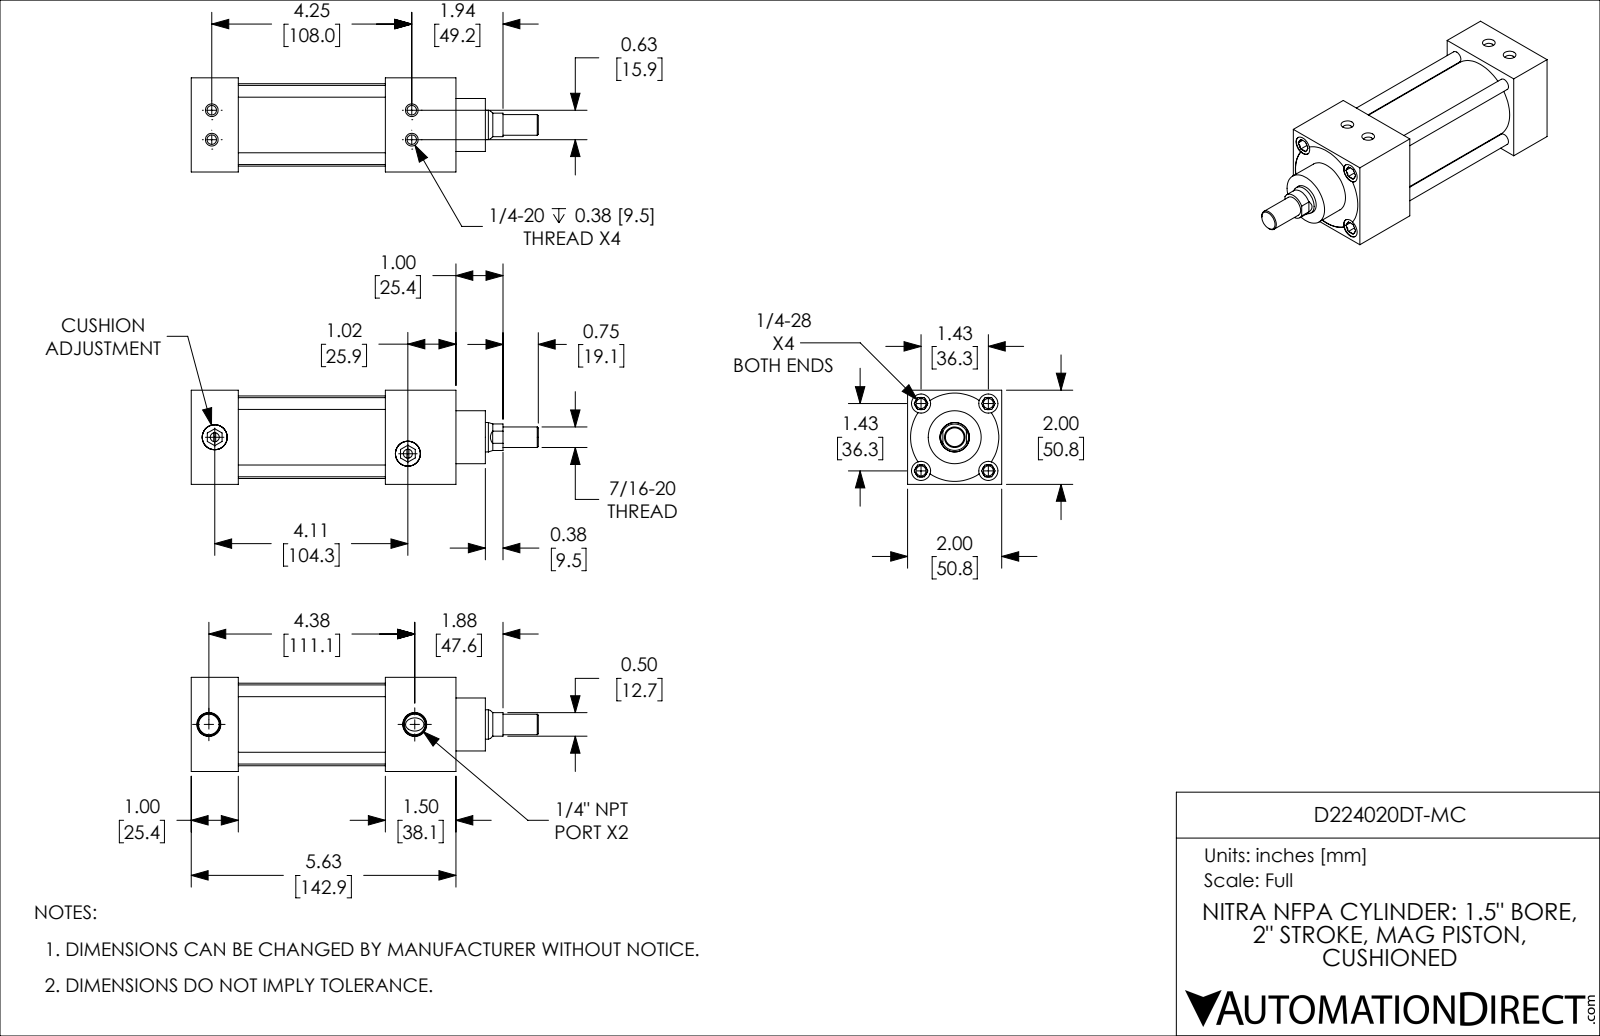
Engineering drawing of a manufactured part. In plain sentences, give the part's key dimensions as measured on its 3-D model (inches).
The part is named "D224020DT-MC_PISTON_KK1; D224020DT-MC; D224020DT-MC_CUSHION; D224020DT-MC_BODY". Its 3-D file was written by "SolidWorks 2019 (CONFIG_CONTROL_DESIGN)". It is 4 solids with 251 faces: 90 planar, 81 cylindrical and 80 other. Overall it measures 7.375 by 2 by 2 inches. Its volume is 15.46 cubic inches and its surface area 109.5 square inches. Round holes: 4 of diameter 0.201, 4 of diameter 0.213, 4 of diameter 0.406, 2 of diameter 0.19, 2 of diameter 0.438, 2 of diameter 0.531, 1 of diameter 0.626, 1 of diameter 1.501. Round bosses or shafts: 4 of diameter 0.25, 2 of diameter 0.532, 1 of diameter 1.751, 1 of diameter 1.499, 1 of diameter 1.125, 1 of diameter 0.624, 1 of diameter 0.437. Partial cylindrical surfaces (rounded edges, fillets, slot ends): 1 of radius 0.281, 1 of radius 0.937. The main face-to-face distances are 2, 1, 4.125, 3.125, 5.62, 4.62, 1.495, 2.125, 1.125, 3.495. The hole center spacings are 0.319, 1.011, 1.43, 0.625, 2.022, 4.25, 4.296, 4.324.
